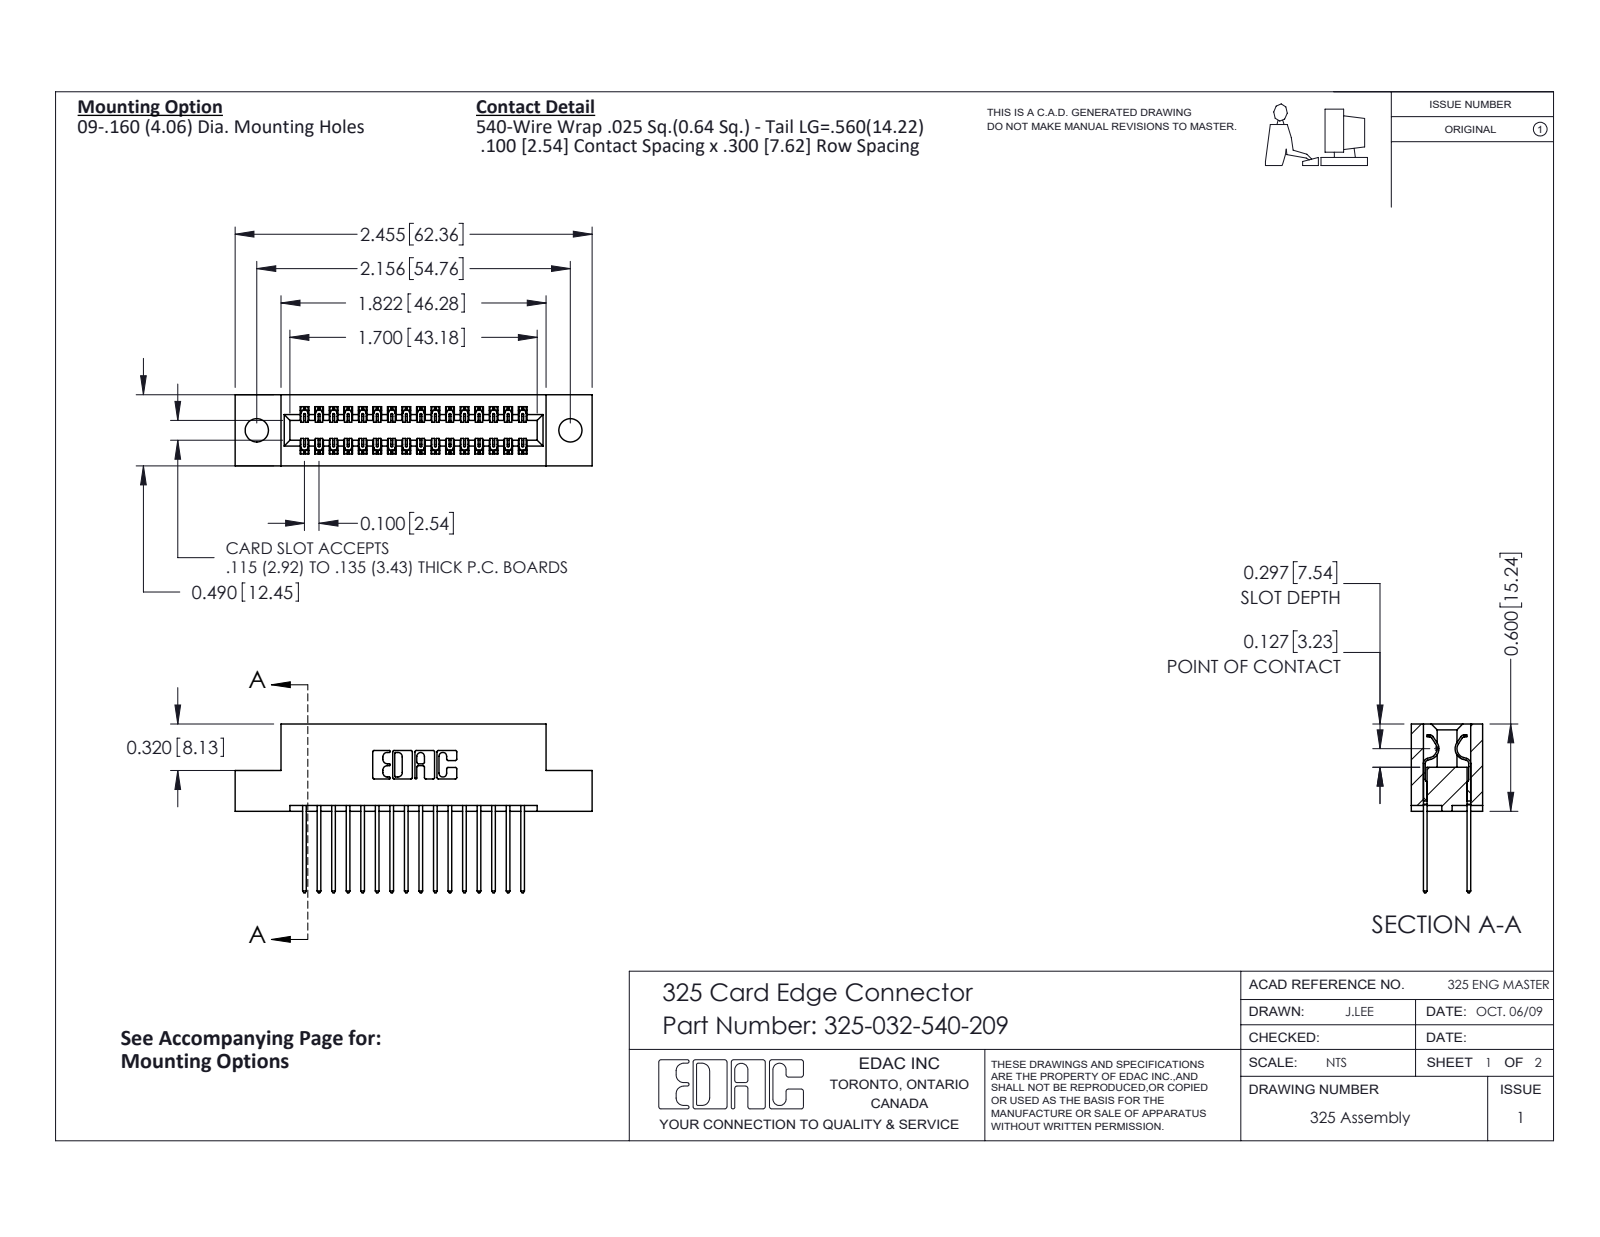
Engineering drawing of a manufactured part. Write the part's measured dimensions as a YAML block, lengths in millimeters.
part_name: "325 Part_.160 TH; 325-292-001_325-293-140; 325-032-540-209"
step_written_by: "SolidWorks 2016 (CONFIG_CONTROL_DESIGN)"
units: millimeters
bodies: {solids: 33, faces: 1778, planar: 1222, cylindrical: 556, other: 0}
overall_size: [62.4, 29.5, 12.4]
volume: 7700
surface_area: 9213
round_holes:
  - {diameter: 4.1, count: 2}
partial_cylinders:
  - {radius: 0.2, count: 48}
  - {radius: 0.3, count: 32}
  - {radius: 0.3, count: 22}
  - {radius: 0.2, count: 6}
  - {radius: 0.8, count: 6}
  - {radius: 0.7, count: 3}
  - {radius: 0.4, count: 2}
  - {radius: 0.6, count: 2}
face_to_face_distances: [2.1, 10.3, 7.6, 2.7, 9.7, 0.6, 12.4, 8.3, 1, 15.2]
hole_center_spacings: [54.8]
